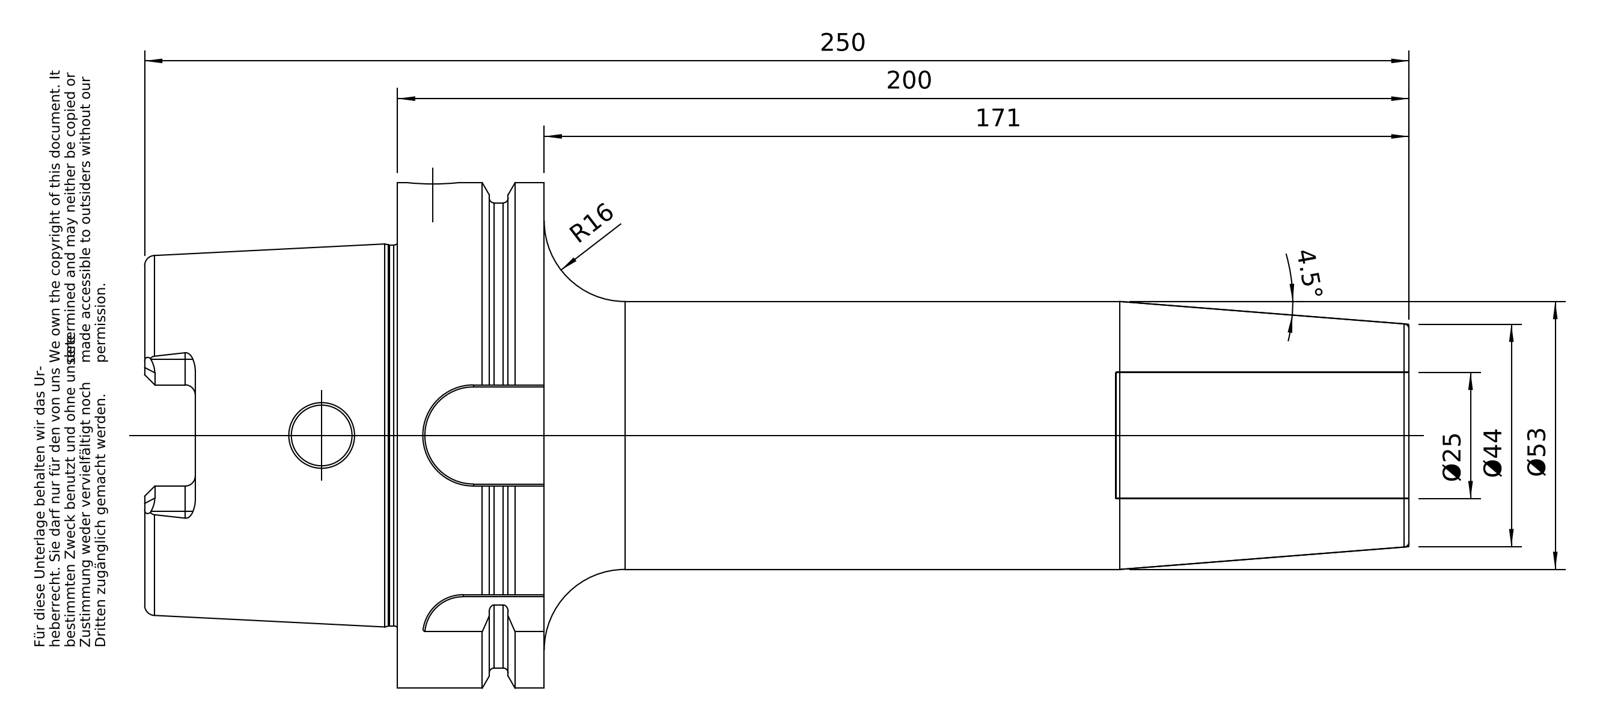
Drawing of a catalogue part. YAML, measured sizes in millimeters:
part_name: "A100-146-25"
step_written_by: "PRO/ENGINEER BY PARAMETRIC TECHNOLOGY CORPORATION, 2010430 (CONFIG_CONTROL_DESIGN)"
units: millimeters
bodies: {solids: 1, faces: 174, planar: 50, cylindrical: 51, other: 73}
overall_size: [250, 100, 100]
volume: 593145
surface_area: 80718
round_holes:
  - {diameter: 10, count: 1}
  - {diameter: 12, count: 1}
  - {diameter: 22.5, count: 1}
  - {diameter: 24, count: 1}
  - {diameter: 24.32, count: 1}
  - {diameter: 24.5, count: 1}
  - {diameter: 25, count: 1}
  - {diameter: 53, count: 1}
  - {diameter: 63, count: 1}
round_bosses_or_shafts:
  - {diameter: 100, count: 1}
  - {diameter: 92, count: 1}
  - {diameter: 75.36, count: 1}
partial_cylinders:
  - {radius: 2, count: 6}
  - {radius: 5, count: 4}
  - {radius: 8, count: 1}
  - {radius: 10, count: 1}
  - {radius: 11, count: 1}
face_to_face_distances: [29, 12.5, 16.5, 200, 187.5, 171, 50, 62.5, 79, 250]
